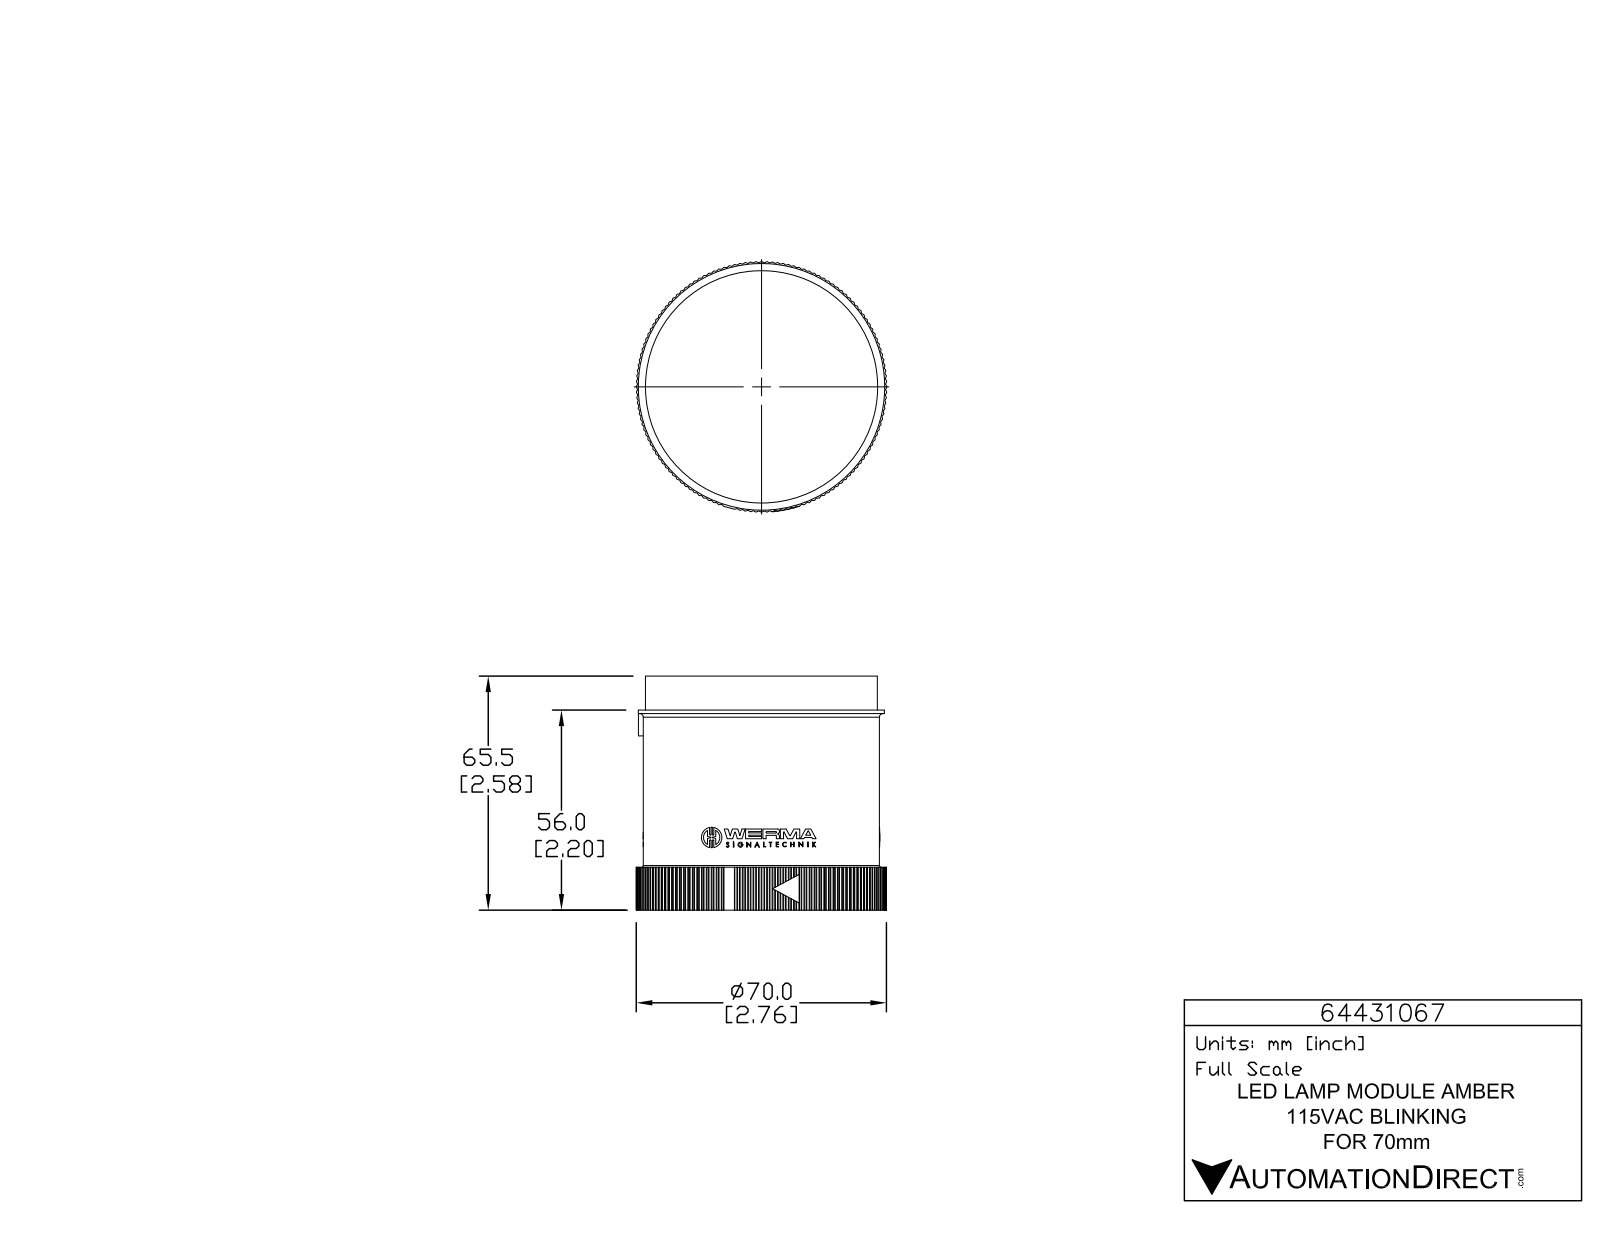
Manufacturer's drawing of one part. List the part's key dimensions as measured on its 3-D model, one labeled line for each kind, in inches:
Part name (STEP PRODUCT): 64431067
STEP written by: SolidWorks 2015 (AUTOMOTIVE_DESIGN)
Units: inches
Bodies: 1 solid, 1400 faces (832 planar, 563 cylindrical, 5 other)
Overall size (bounding box): 2.762 × 2.762 × 2.579
Volume: 12.02 in³ · Surface area: 37.48 in²
Round holes (diameter × count): ⌀0.039 ×3, ⌀2.575 ×1
Round bosses / shafts (diameter × count): ⌀0.226 ×3, ⌀0.056 ×3, ⌀2.717 ×1, ⌀2.606 ×1, ⌀2.559 ×1
Partial cylindrical surfaces — rounded edges, fillets, slot ends (radius × count): R0.008 ×285, R0.008 ×6, R0.008 ×6, R0.008 ×6, R0.131 ×6, R0.004 ×3, R0.005 ×3, R0.008 ×3
Main face-to-face distances: 2.201, 2.451, 0.378, 2.579, 2.205, 1.827, 0.374, 2.452, 0.472, 0.094
